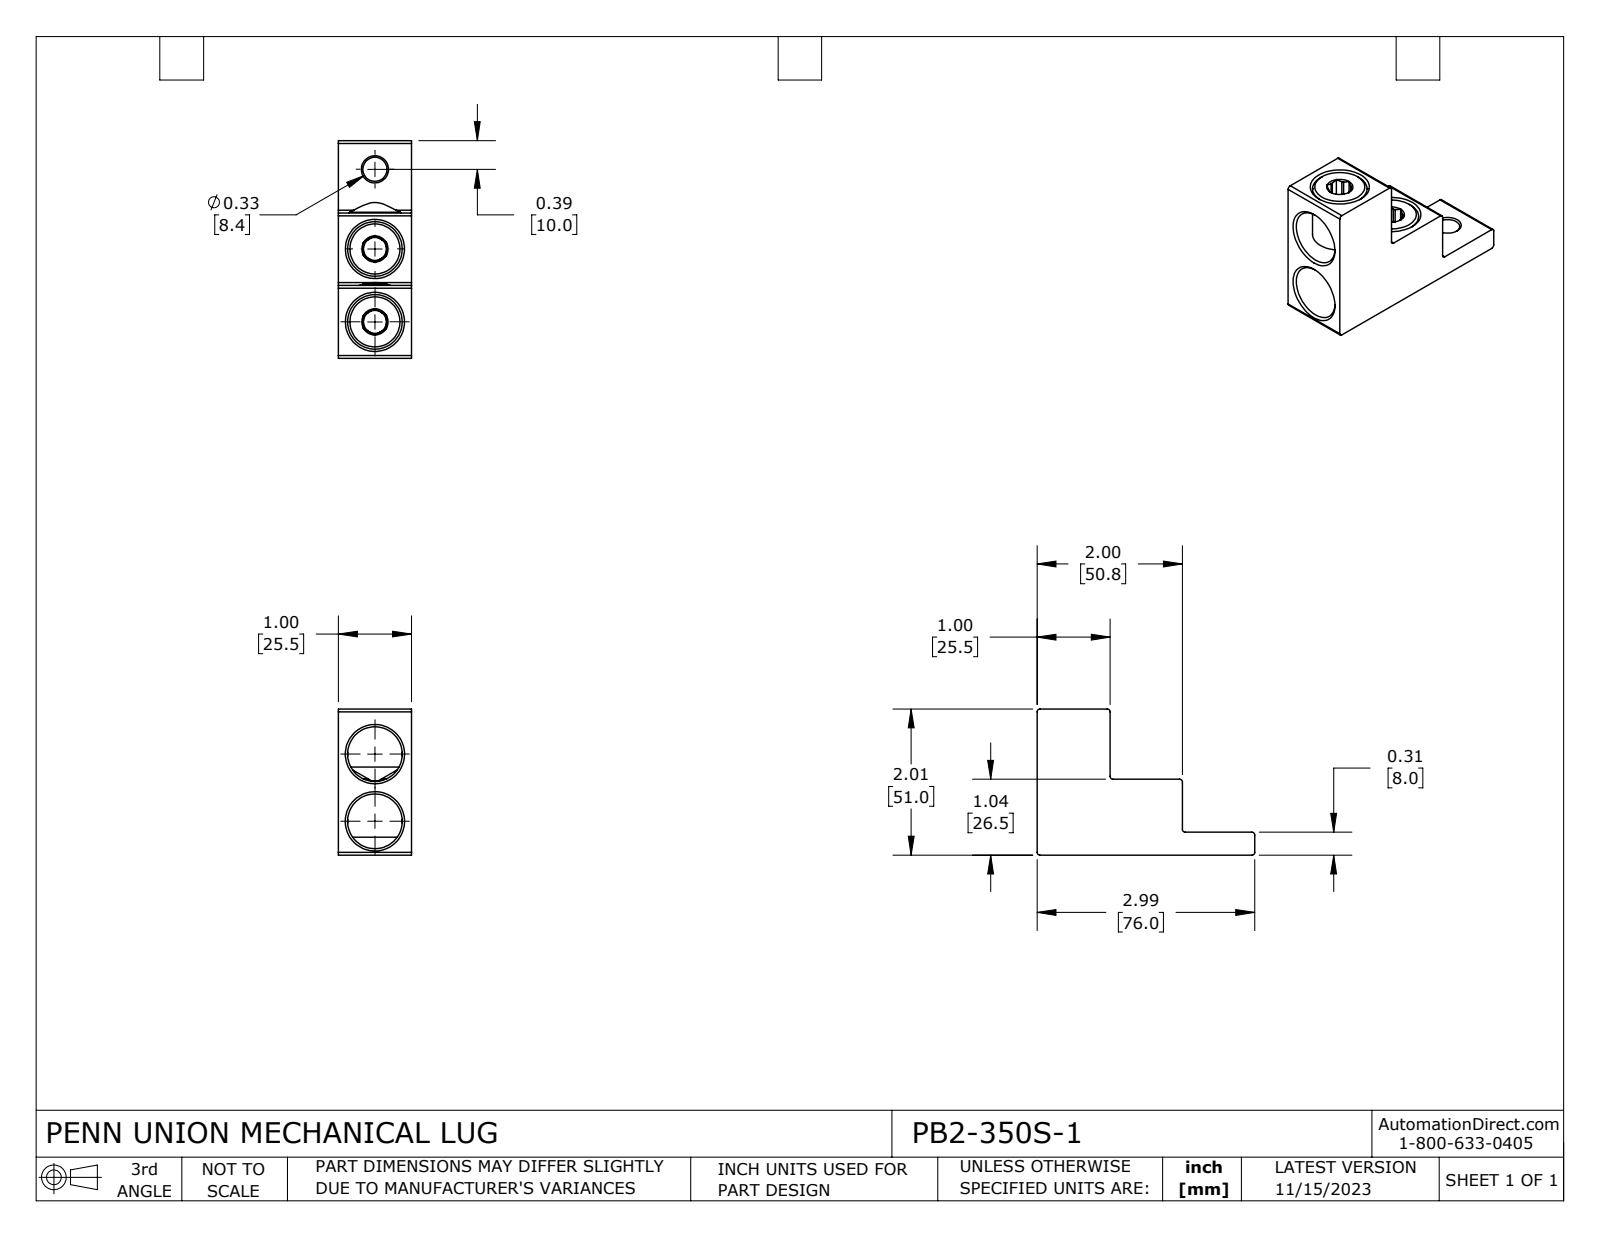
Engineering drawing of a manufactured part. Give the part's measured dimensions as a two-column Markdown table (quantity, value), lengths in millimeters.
| quantity | value |
| --- | --- |
| part name | PB2-350S-1 |
| STEP written by | SolidWorks 2023 (CONFIG_CONTROL_DESIGN) |
| units | millimeters |
| bodies | 3 solids, 118 faces (48 planar, 27 cylindrical, 43 other) |
| overall size | 76 × 51 × 25.5 |
| volume | 40 490 mm³ |
| surface area | 18 430 mm² |
| round holes (diameter × count) | 8 × 2, 17.4 × 2, 19.1 × 2, 8.4 × 1 |
| round bosses / shafts (diameter × count) | 19.1 × 2 |
| partial cylindrical surfaces (radius × count) | 1 × 8 |
| main face-to-face distances | 25.5, 8, 51, 43, 24.5, 26.5, 18.5, 25.2, 50.7, 76 |
| hole center spacings | 23.4, 25.5, 27.8, 53.2 |
